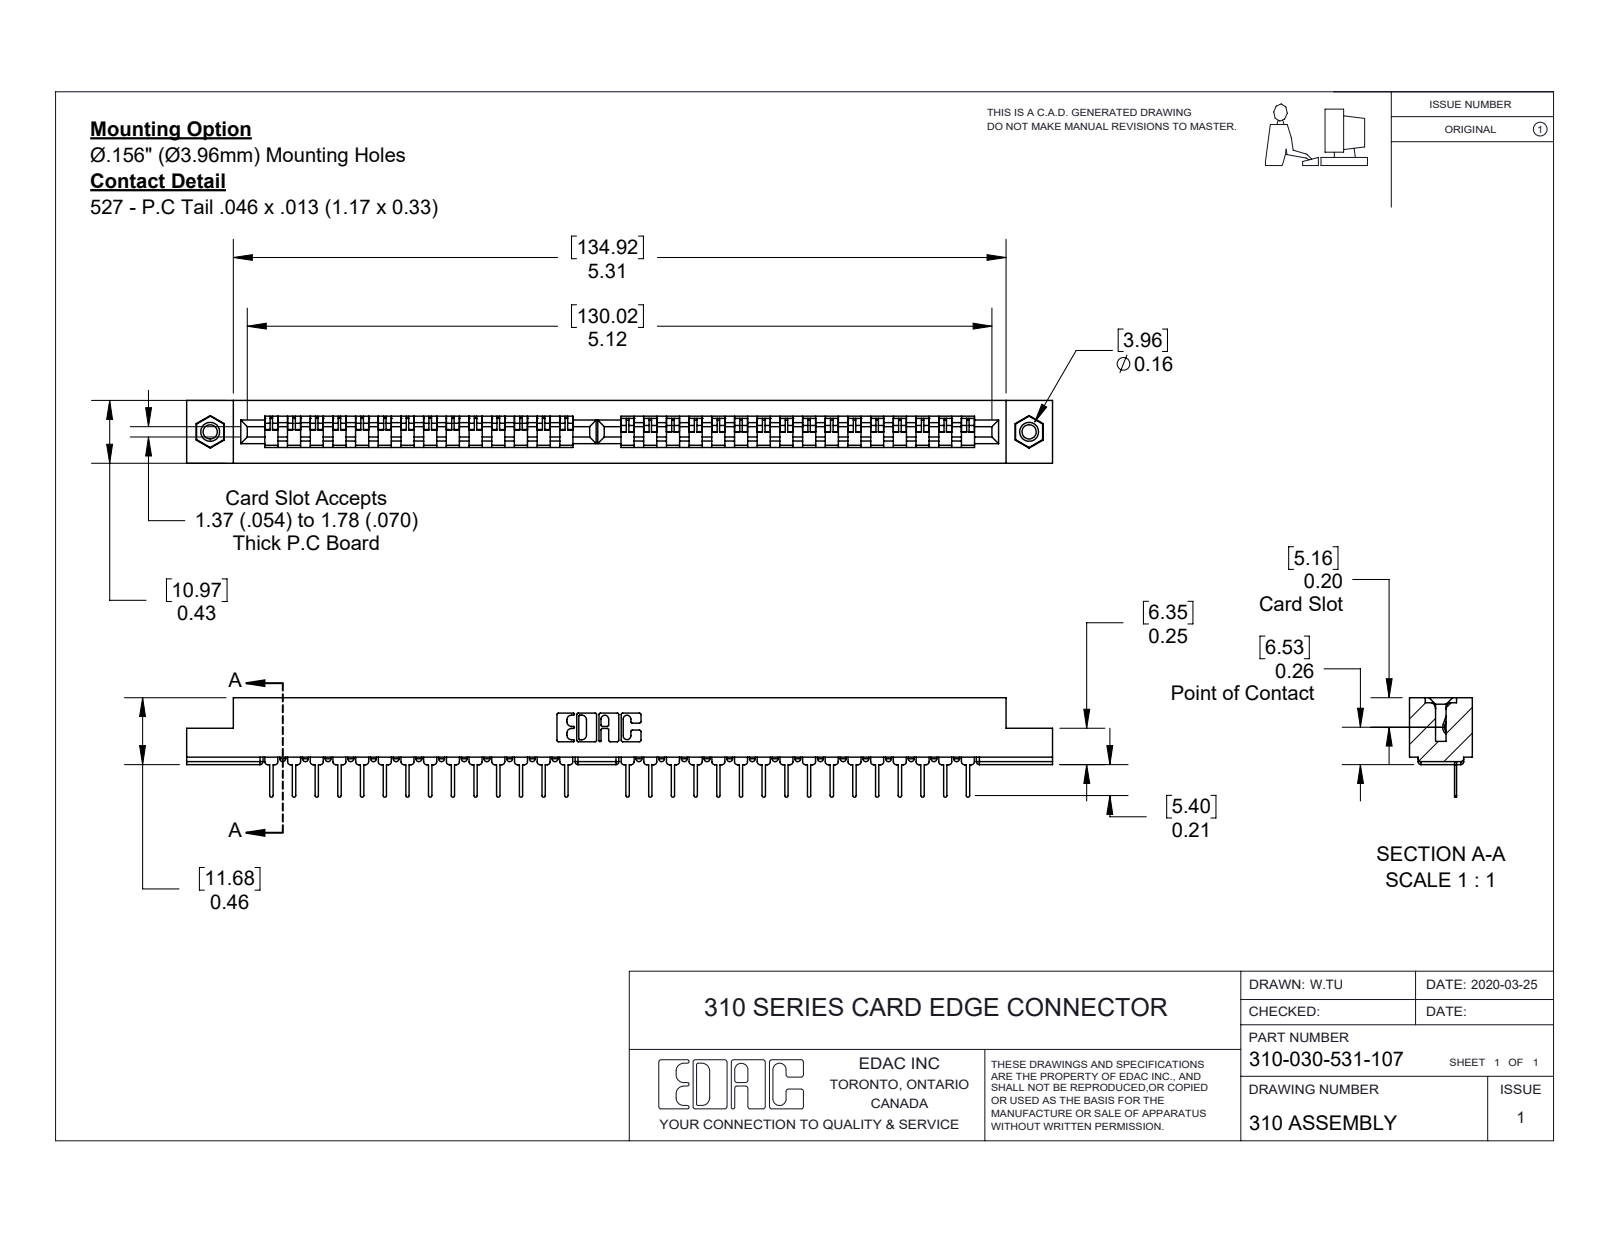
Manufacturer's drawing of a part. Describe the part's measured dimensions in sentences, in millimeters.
The part is named "307-290-001_531; 310-030-531-107; 345-250-001_345-250-005-103; 310 Part_.116 Hex". Its 3-D file was written by "SolidWorks 2016 (CONFIG_CONTROL_DESIGN)". It is 33 solids with 1906 faces: 1226 planar, 600 cylindrical and 80 other. Overall it measures 151.21 by 17.37 by 10.97 millimeters. Its volume is 12 600 cubic millimeters and its surface area 14 667 square millimeters. Round holes: 2 of diameter 2.5, 2 of diameter 3.17, 2 of diameter 3.96. Round bosses or shafts: 2 of diameter 3.94. Partial cylindrical surfaces (rounded edges, fillets, slot ends): 158 of radius 0.51, 30 of radius 0.29, 22 of radius 0.25, 6 of radius 0.17, 6 of radius 0.8, 3 of radius 0.67, 2 of radius 0.3, 2 of radius 0.64. The main face-to-face distances are 2.76, 8.22, 10.98, 1.82, 0.38, 0.33, 10.38, 5.46, 6.4, 4.58. The hole center spacings are 143.
